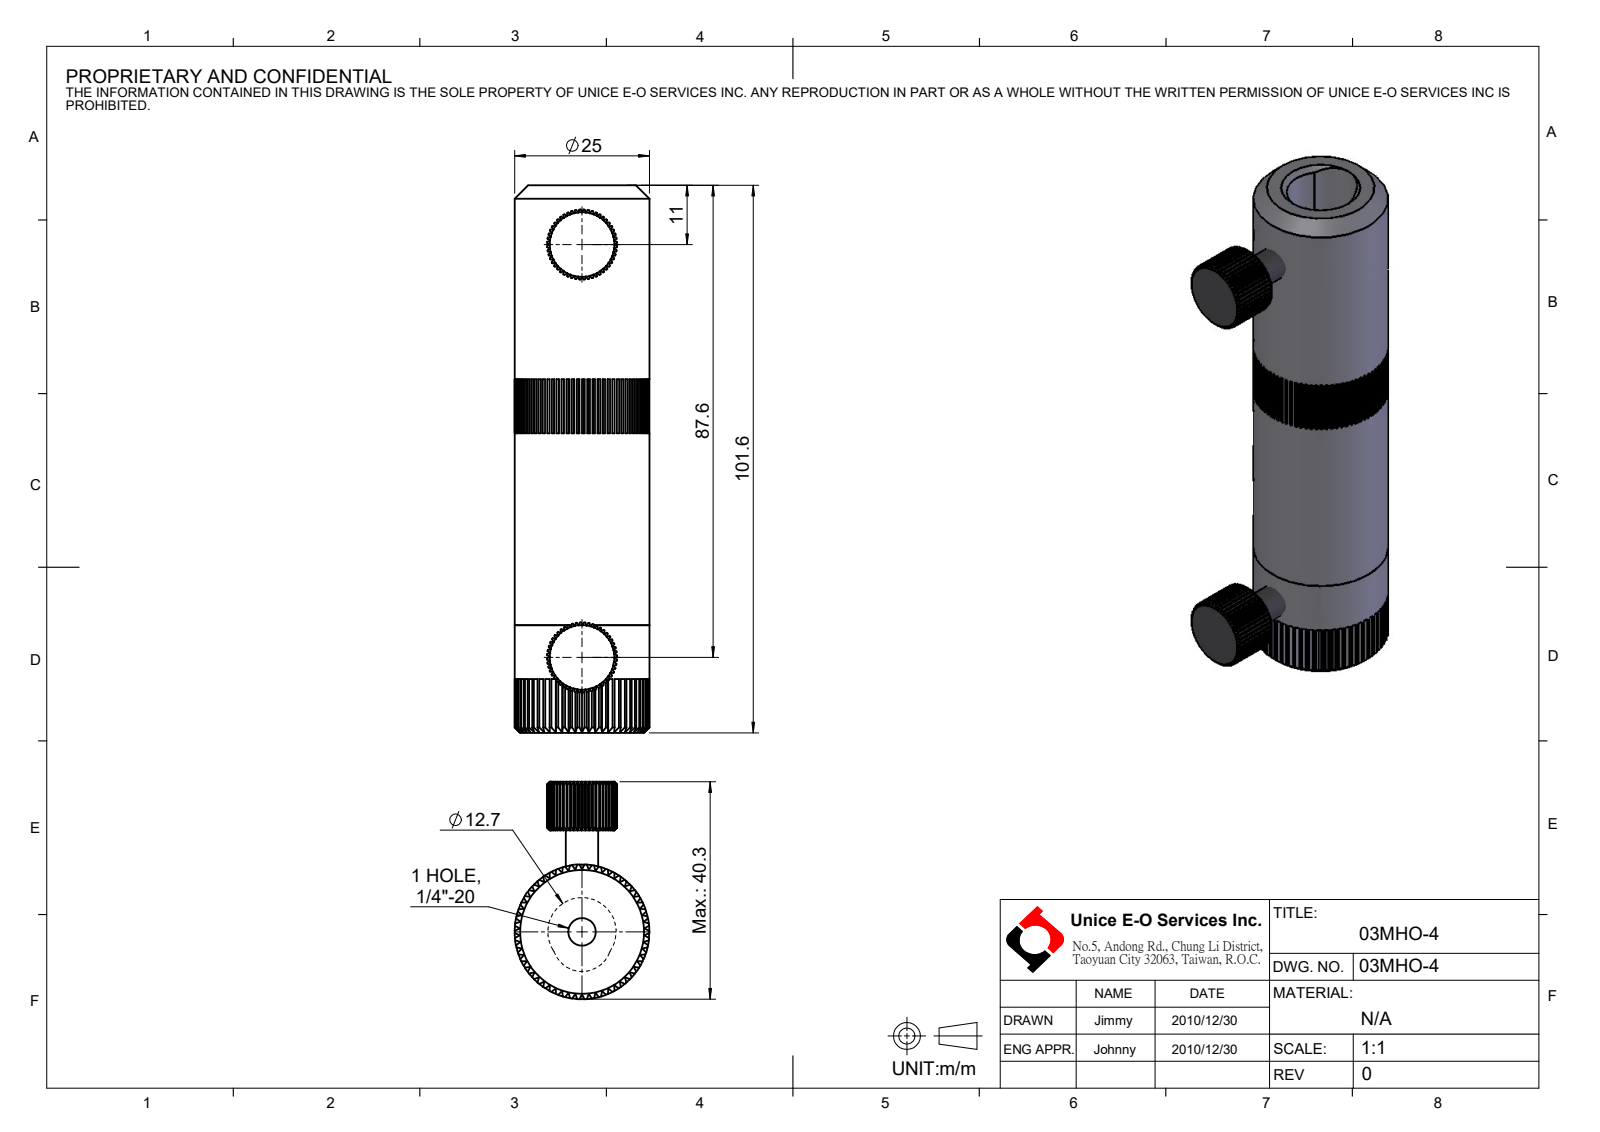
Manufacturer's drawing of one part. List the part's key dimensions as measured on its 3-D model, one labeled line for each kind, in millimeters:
Part name (STEP PRODUCT): 03MHO-4
STEP written by: SolidWorks 2016 (CONFIG_CONTROL_DESIGN)
Units: millimetres
Bodies: 0 solids, 990 faces (657 planar, 118 cylindrical, 215 other)
Overall size (bounding box): 101.6 × 40.34 × 25
Round holes (diameter × count): ⌀5.11 ×1
Round bosses / shafts (diameter × count): ⌀6 ×2, ⌀25 ×1
Partial cylindrical surfaces — rounded edges, fillets, slot ends (radius × count): R6.5 ×2, R5.5 ×1, R6.35 ×1
Main face-to-face distances: 10.46, 20, 5.39, 5.4, 9, 101.6, 81.6, 10.48, 10, 91.6
